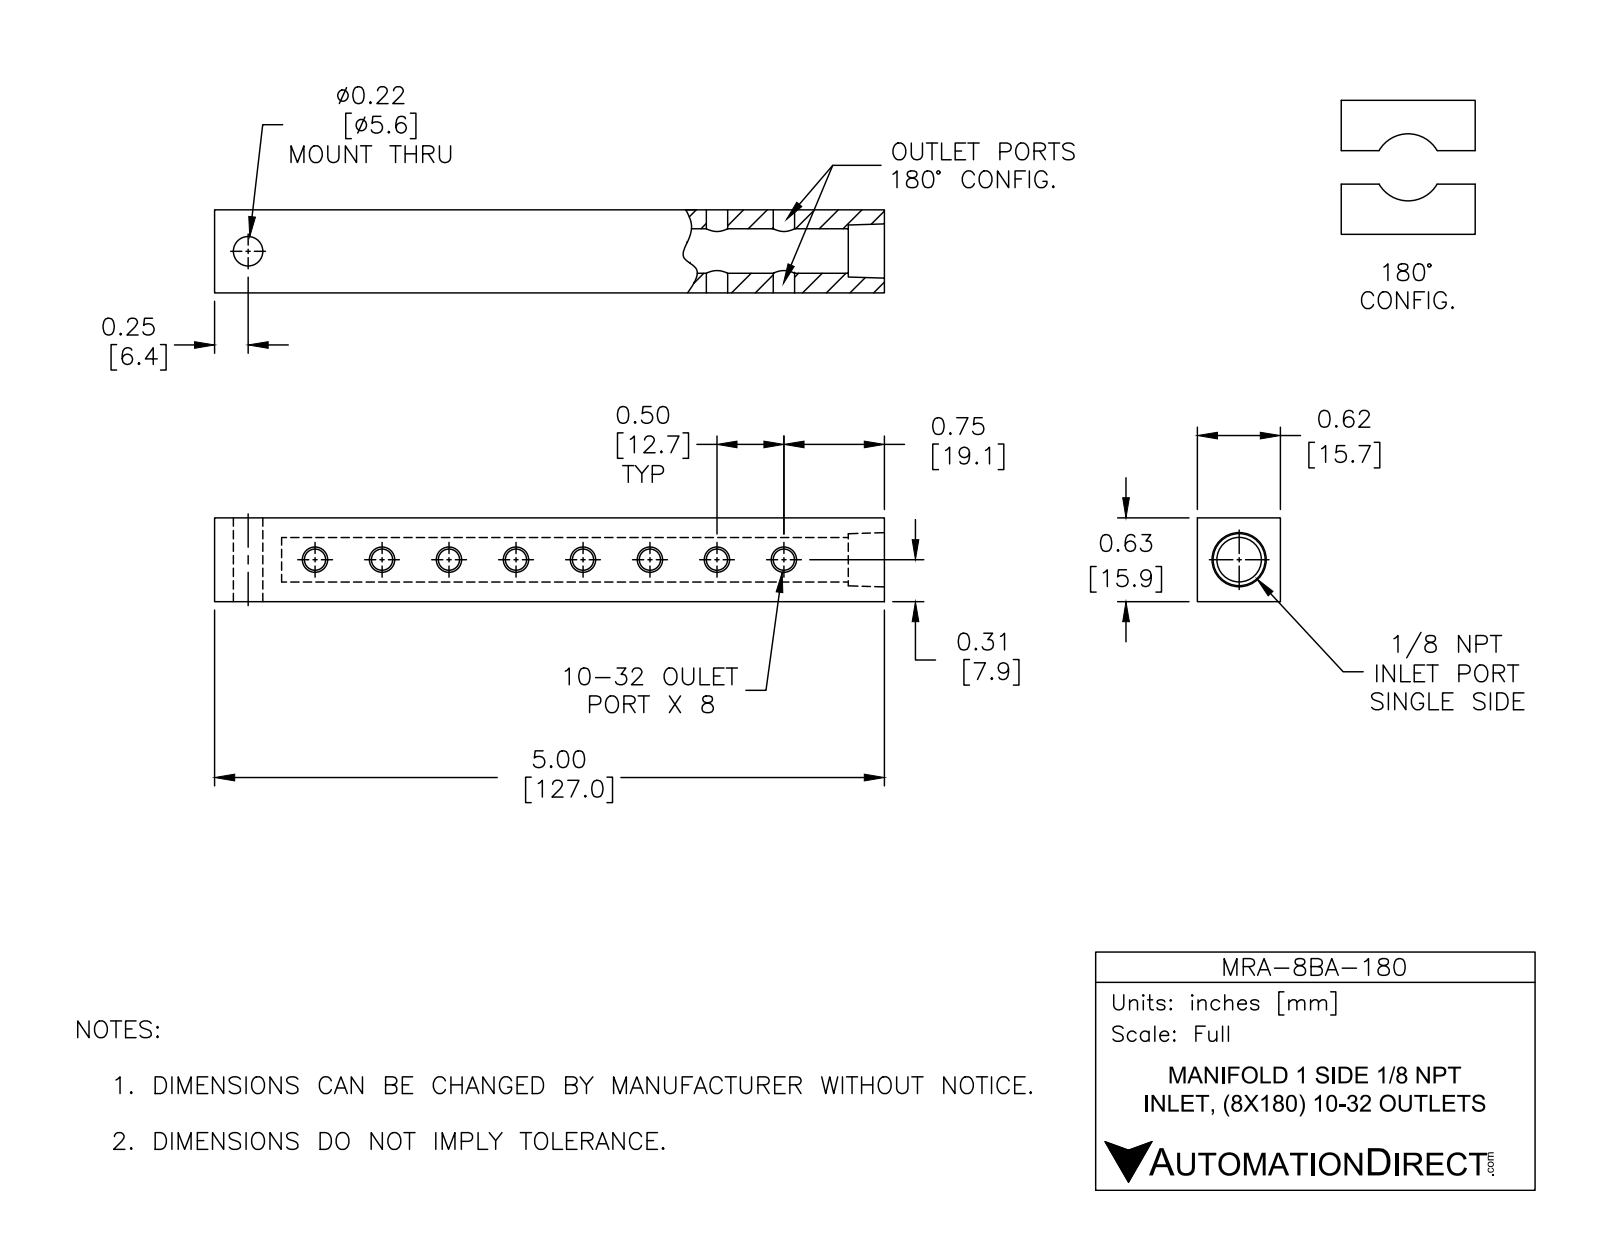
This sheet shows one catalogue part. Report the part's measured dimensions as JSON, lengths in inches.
{"part_name": "MRA-8BA-180", "step_written_by": "SolidWorks 2015 (CONFIG_CONTROL_DESIGN)", "units": "inches", "bodies": {"solids": 1, "faces": 46, "planar": 8, "cylindrical": 36, "other": 2}, "overall_size": [5, 0.625, 0.62], "volume_in3": 1.467, "surface_area_in2": 18.9, "round_holes": [[0.159, 8], [0.22, 1], [0.332, 1]], "face_to_face_distances": [0.625, 0.62, 5, 0.5, 4.5, 4.73, 4.23, 0.27], "hole_center_spacings": [0.5, 1, 1.5, 2, 2.5, 3, 3.5]}
